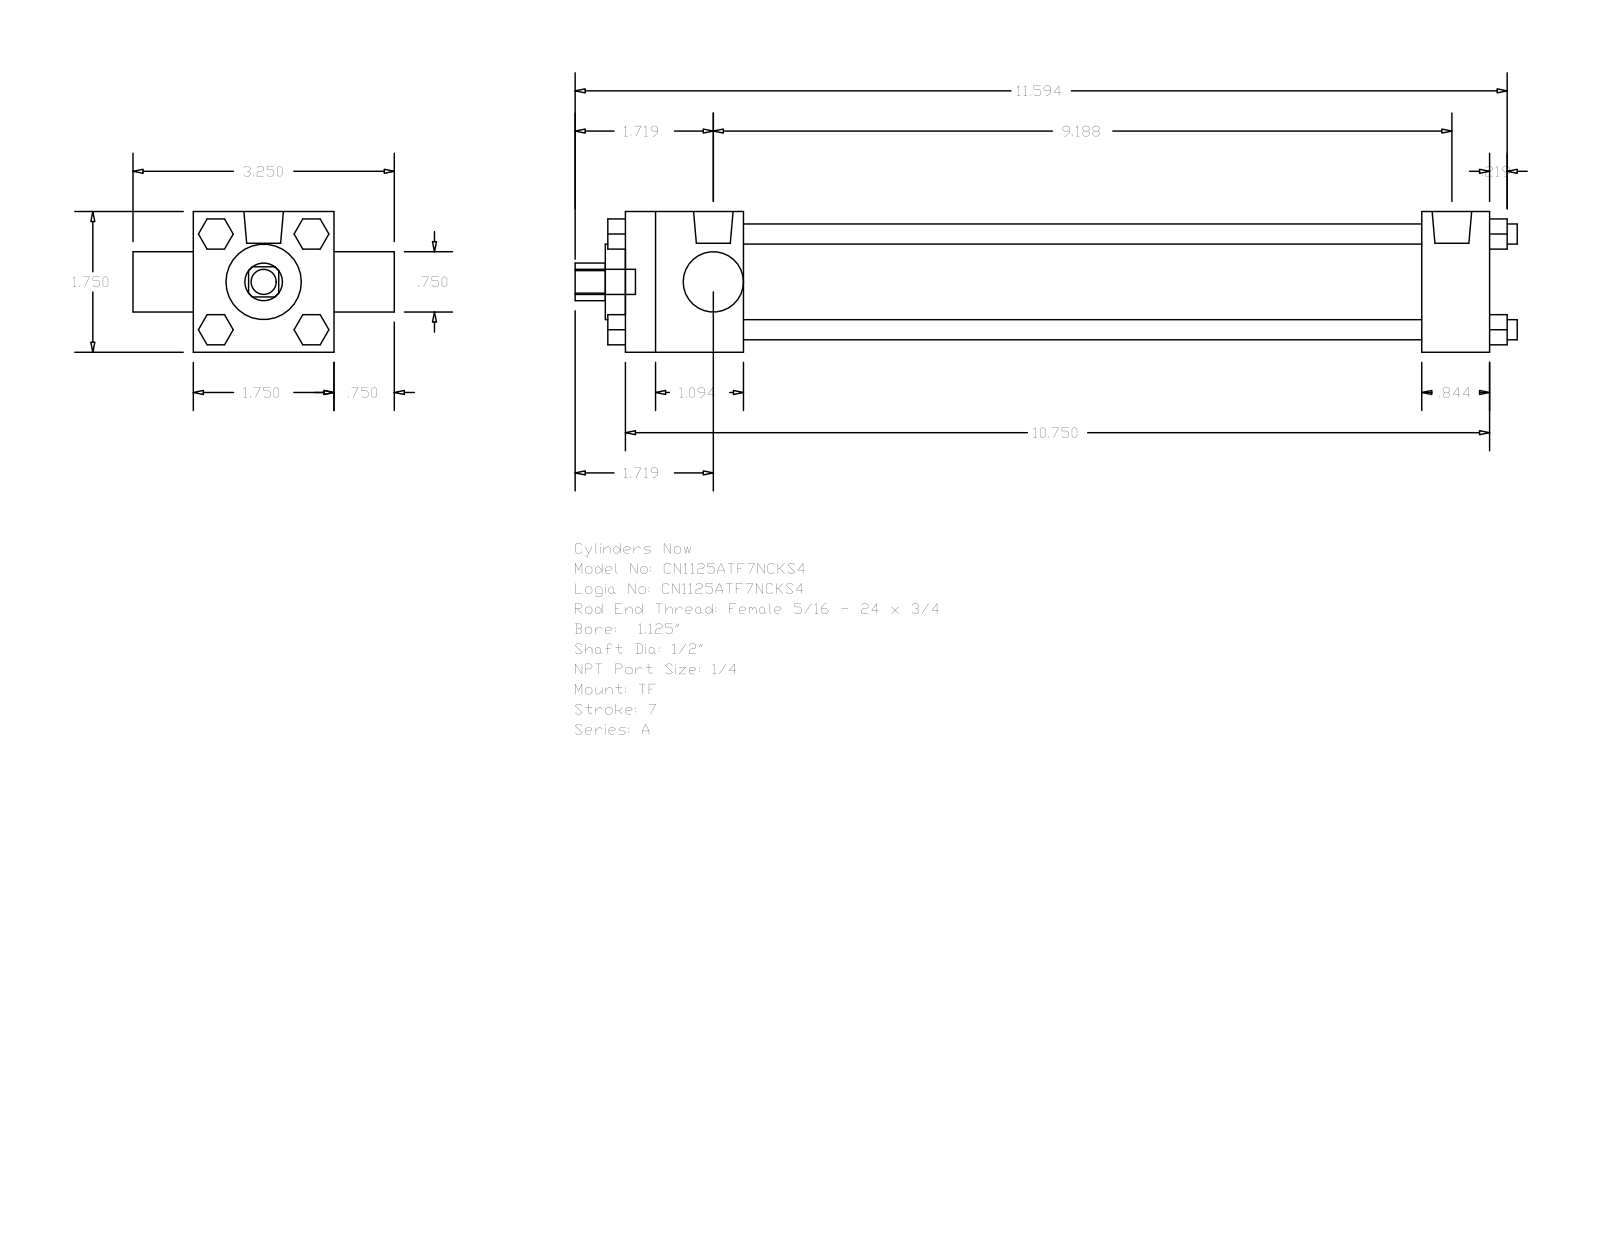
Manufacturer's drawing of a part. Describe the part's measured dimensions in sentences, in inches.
The part is named "A_TF__0112_0.5". Its 3-D file was written by "GSSL Pune (CONFIG_CONTROL_DESIGN)". It is 0 solids with 120 faces: 92 planar, 28 cylindrical and 0 other. Overall it measures 11.719 by 3.25 by 1.75 inches. Round holes: 1 of diameter 0.5, 1 of diameter 0.75, 1 of diameter 0.937, 1 of diameter 1.255. Round bosses or shafts: 4 of diameter 0.25, 3 of diameter 0.219, 2 of diameter 0.492, 1 of diameter 0.313. Partial cylindrical surfaces (rounded edges, fillets, slot ends): 1 of radius 0.234. The main face-to-face distances are 1.75, 10.75, 9.906, 0.844, 1.469, 8.437, 9.281, 0.75, 2.5, 0.375.
